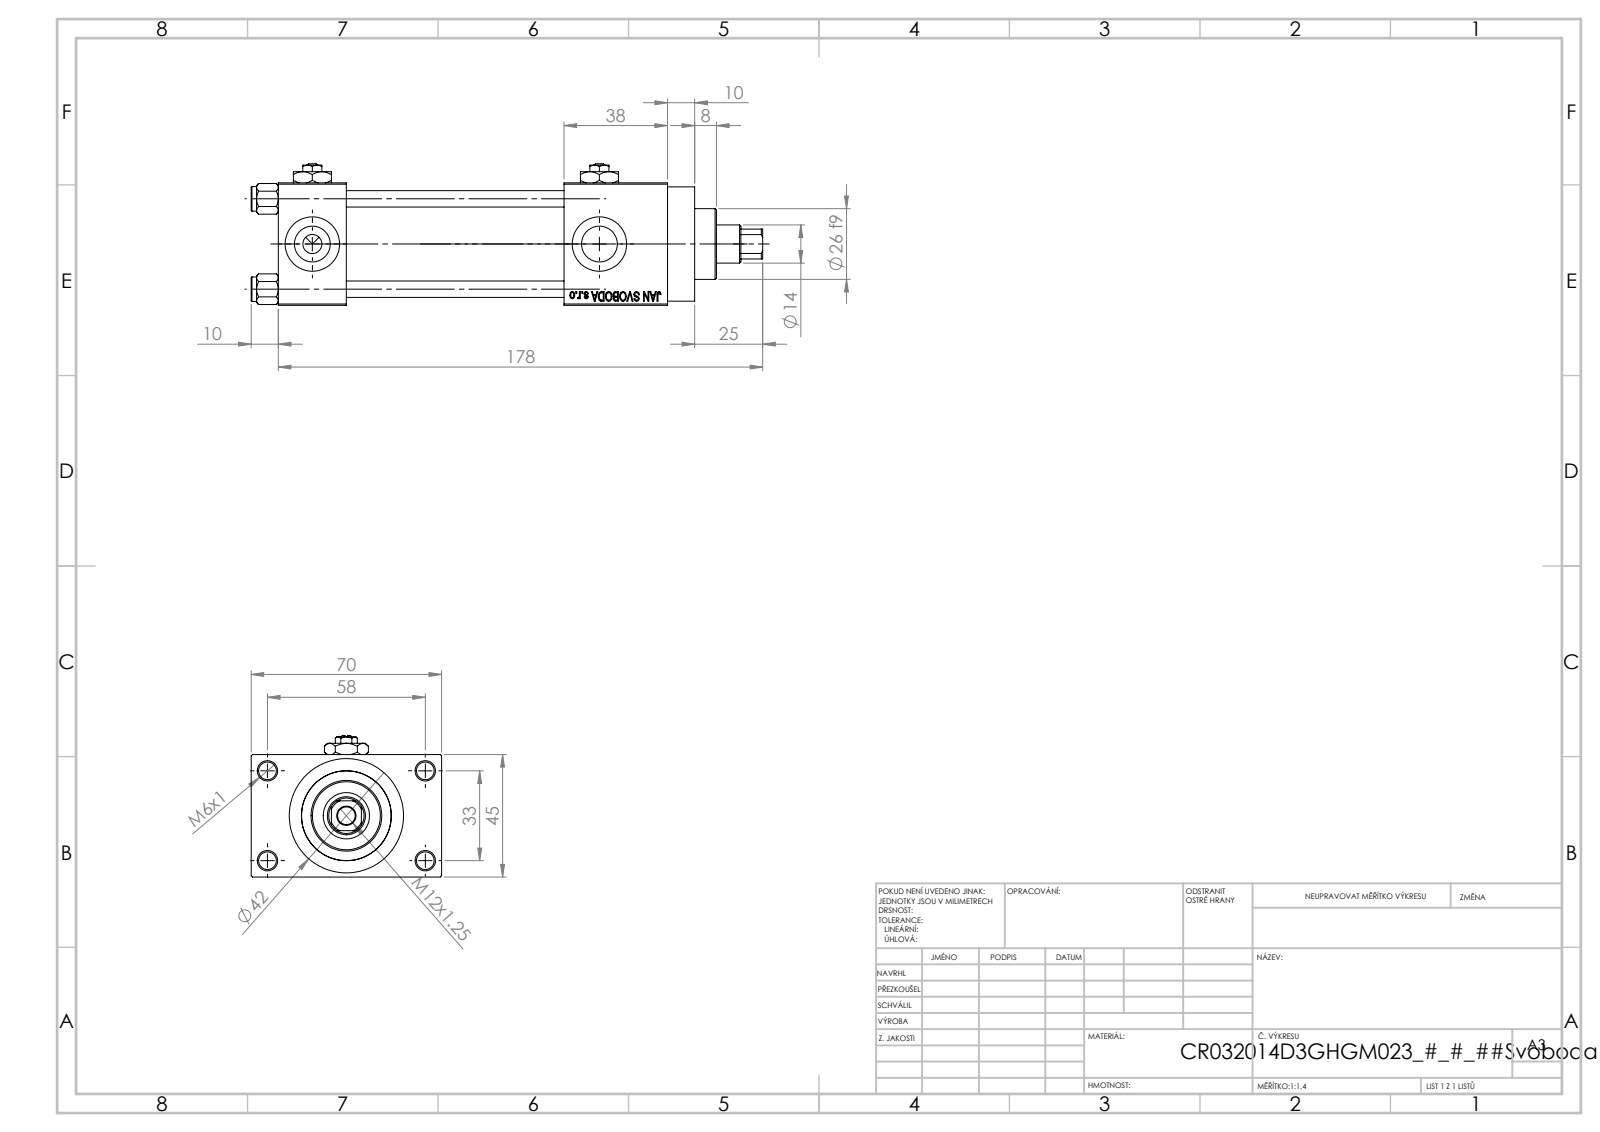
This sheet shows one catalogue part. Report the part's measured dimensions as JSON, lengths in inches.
{"part_name": "V215CR_D_Body; V215CR_VCP_D; V215_VC_A; Zatka_pro_OIL_PORT (+2 more)", "step_written_by": "SolidWorks 2019 (CONFIG_CONTROL_DESIGN)", "units": "inches", "bodies": {"solids": 13, "faces": 1201, "planar": 542, "cylindrical": 99, "other": 560}, "overall_size": [7.402, 2.756, 2.047], "volume_in3": 15.07, "surface_area_in2": 135.3, "round_holes": [[0.256, 5], [0.236, 4], [0.518, 4], [0.787, 4], [0.276, 3], [0.551, 1], [0.669, 1], [0.945, 1], [1.26, 1], [1.299, 1]], "round_bosses_or_shafts": [[0.354, 4], [1.654, 1], [1.496, 1], [1.024, 1]], "partial_cylinders_radius": [[0.256, 1]], "face_to_face_distances": [1.772, 0.984, 0.492, 3.15, 4.134, 2.264, 4.646, 1.496, 5.63, 2.756], "hole_center_spacings": [0.488, 0.924, 1.307, 1.314, 1.392, 1.795, 2.219, 1.299]}
